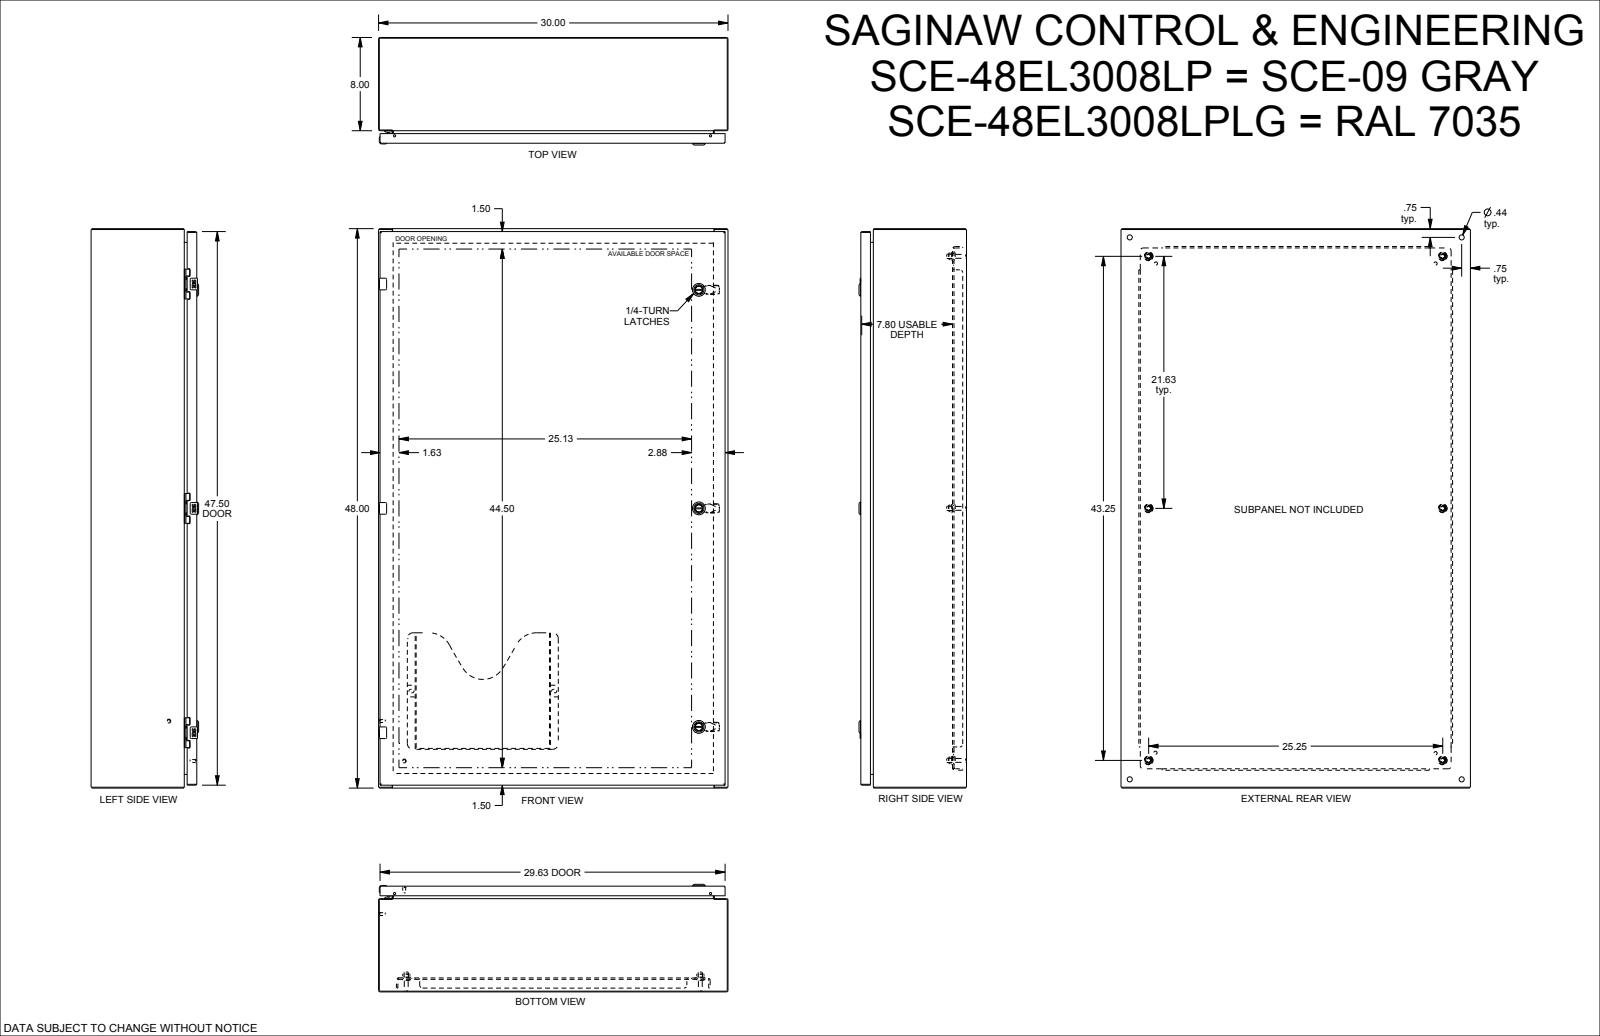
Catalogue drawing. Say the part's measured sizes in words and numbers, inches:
The part is named "SCE-48EL3008LPLG". Its 3-D file was written by "SolidWorks 2019 (CONFIG_CONTROL_DESIGN)". It is 0 solids with 3818 faces: 1807 planar, 1058 cylindrical and 953 other. Overall it measures 48 by 30 by 9.23 inches. Round holes: 6 of diameter 0.172, 6 of diameter 0.205, 6 of diameter 0.244, 6 of diameter 0.266, 6 of diameter 0.367, 6 of diameter 0.375, 6 of diameter 0.5, 4 of diameter 0.281, 4 of diameter 0.437, 3 of diameter 0.04, 3 of diameter 0.156, 3 of diameter 0.197. Round bosses or shafts: 9 of diameter 0.17, 6 of diameter 0.366, 6 of diameter 0.332, 6 of diameter 0.25, 6 of diameter 0.24, 4 of diameter 0.248, 4 of diameter 0.196, 3 of diameter 1.102. Partial cylindrical surfaces (rounded edges, fillets, slot ends): 82 of radius 0.012, 40 of radius 0.01, 32 of radius 0.015, 28 of radius 0.02, 17 of radius 0.04, 16 of radius 0.025, 16 of radius 0.1, 15 of radius 0.03. The main face-to-face distances are 0.075, 0.075, 8.923, 8.998, 9.073, 8.998, 1.2, 7.873, 0.125, 1. The hole center spacings are 19.25, 0.985, 38.5, 0.02, 0.493, 0.494, 4.493, 18.265.
